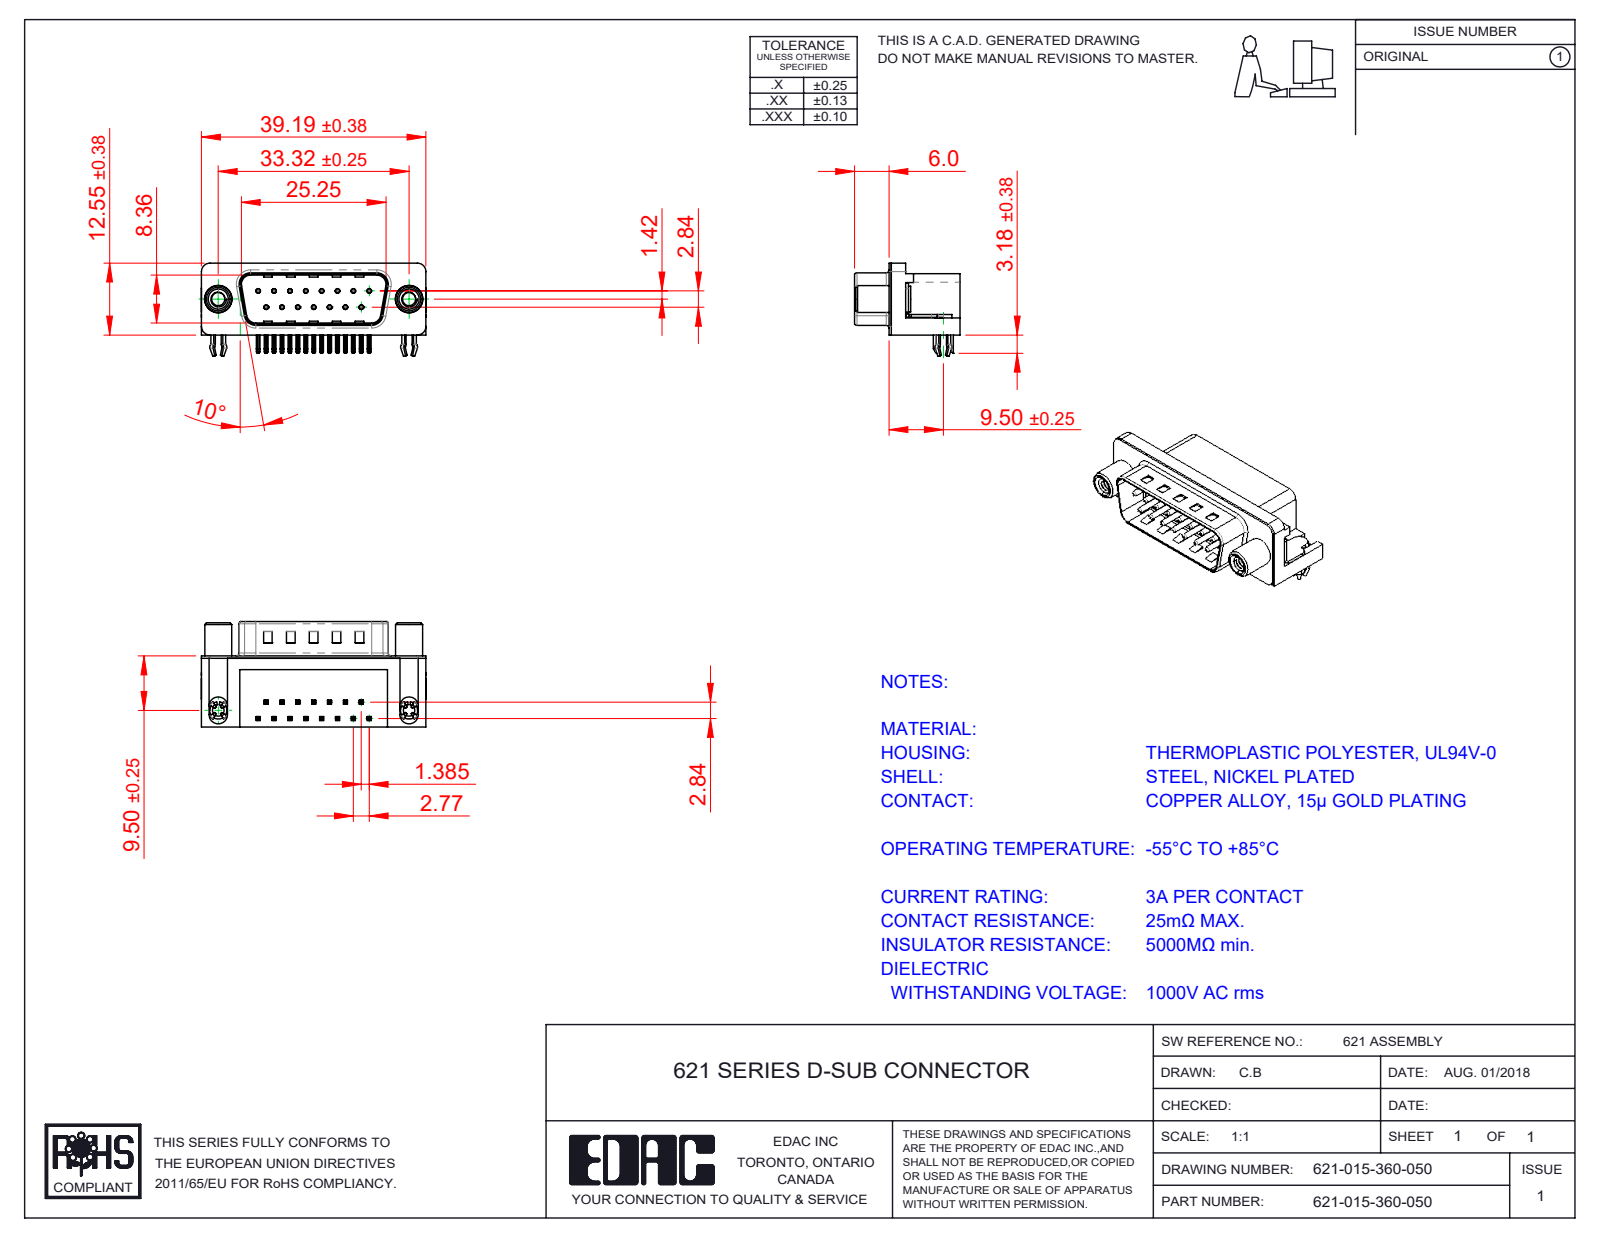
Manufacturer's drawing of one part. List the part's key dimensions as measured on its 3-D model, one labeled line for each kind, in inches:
Part name (STEP PRODUCT): 621 Round Threaded Standoff; 621 Contact Top; 621 Shell_15 Socket; 621 Housing_15 Socket (+3 more)
STEP written by: SolidWorks 2016 (CONFIG_CONTROL_DESIGN)
Units: inches
Bodies: 21 solids, 1501 faces (885 planar, 465 cylindrical, 151 other)
Overall size (bounding box): 1.544 × 0.724 × 0.619
Volume: 0.276 in³ · Surface area: 9.19 in²
Round holes (diameter × count): ⌀0.014 ×15, ⌀0.031 ×15, ⌀0.089 ×2, ⌀0.091 ×2, ⌀0.122 ×2, ⌀0.157 ×2, ⌀0.189 ×2, ⌀0.197 ×2
Round bosses / shafts (diameter × count): ⌀0.03 ×15, ⌀0.193 ×2, ⌀0.185 ×2, ⌀0.177 ×2, ⌀0.152 ×2, ⌀0.128 ×2
Partial cylindrical surfaces — rounded edges, fillets, slot ends (radius × count): R0.01 ×60, R0.005 ×30, R0.039 ×16, R0.02 ×9, R0.063 ×8, R0.059 ×6, R0.035 ×4, R0.079 ×4
Main face-to-face distances: 0.016, 0.472, 0.407, 0.083, 0.412, 0.067, 0.488, 0.428, 0.345, 0.114
Hole centre spacings: 0.124, 0.109, 0.218, 0.327, 0.436, 0.198, 0.198, 0.294
